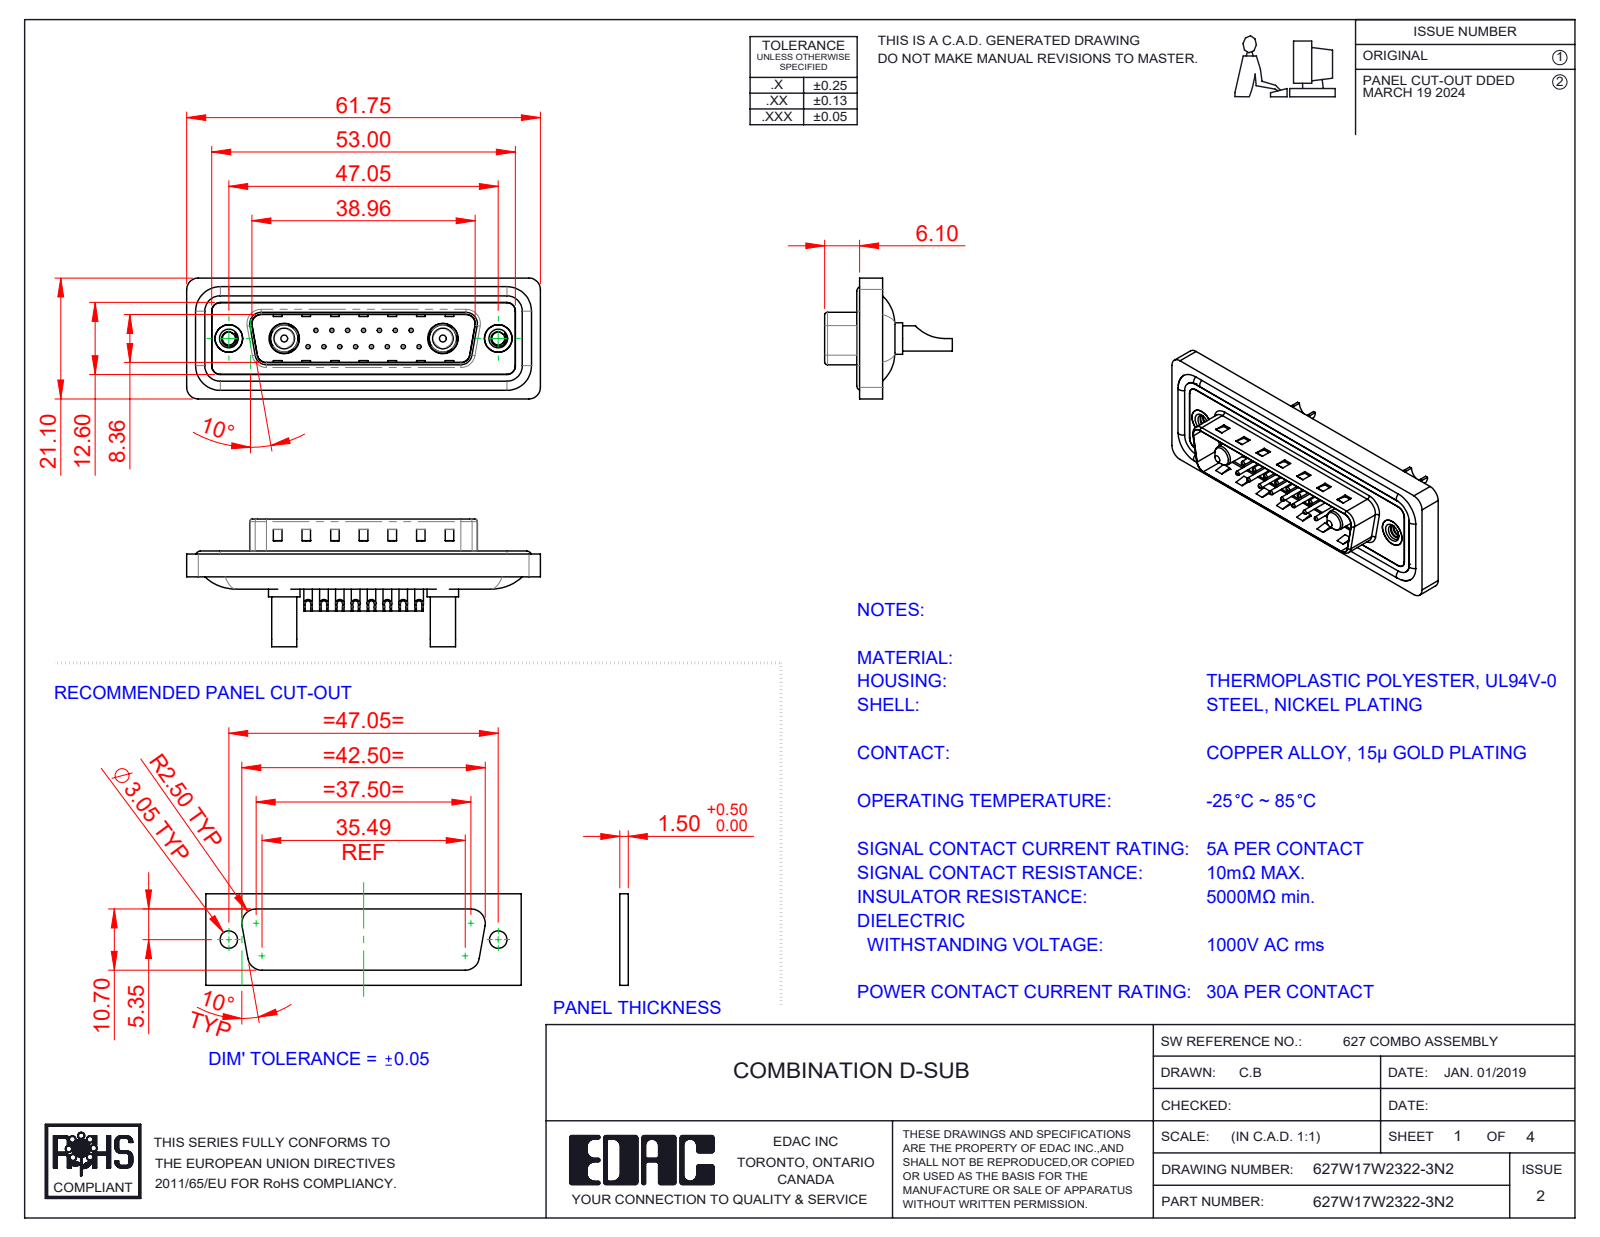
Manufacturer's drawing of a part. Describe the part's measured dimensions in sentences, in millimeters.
The part is named "627Combo Threaded Rivet_2; 627Combo Shell Front_25 Contacts; 627W17W2322-3N2; 627Combo Waterproof Housing_25 Contacts (+5 more)". Its 3-D file was written by "SolidWorks 2023 (CONFIG_CONTROL_DESIGN)". It is 26 solids with 1128 faces: 370 planar, 472 cylindrical and 286 other. Overall it measures 61.75 by 22.3 by 21.1 millimeters. Its volume is 7 338 cubic millimeters and its surface area 12 248 square millimeters. Round holes: 15 of diameter 0.75, 15 of diameter 1, 15 of diameter 1.6, 15 of diameter 2, 2 of diameter 2.26, 2 of diameter 3.5, 2 of diameter 4, 2 of diameter 4.8, 2 of diameter 4.85, 2 of diameter 5, 2 of diameter 5.3. Round bosses or shafts: 15 of diameter 1.5, 4 of diameter 1.6, 2 of diameter 5.5, 2 of diameter 5.2, 2 of diameter 4.9, 2 of diameter 4.75, 2 of diameter 4.4, 2 of diameter 3.75. Partial cylindrical surfaces (rounded edges, fillets, slot ends): 22 of radius 1.5, 18 of radius 2, 8 of radius 0.5, 8 of radius 1.6, 6 of radius 1, 4 of radius 0.25, 4 of radius 0.6, 4 of radius 0.65. The main face-to-face distances are 0.4, 1.5, 1.1, 1.6, 0.5, 3.1, 2.9, 0.82, 9.58, 4.1. The hole center spacings are 3.16, 2.77, 5.54, 8.31, 5.04, 7.49, 11.08, 5.03.
